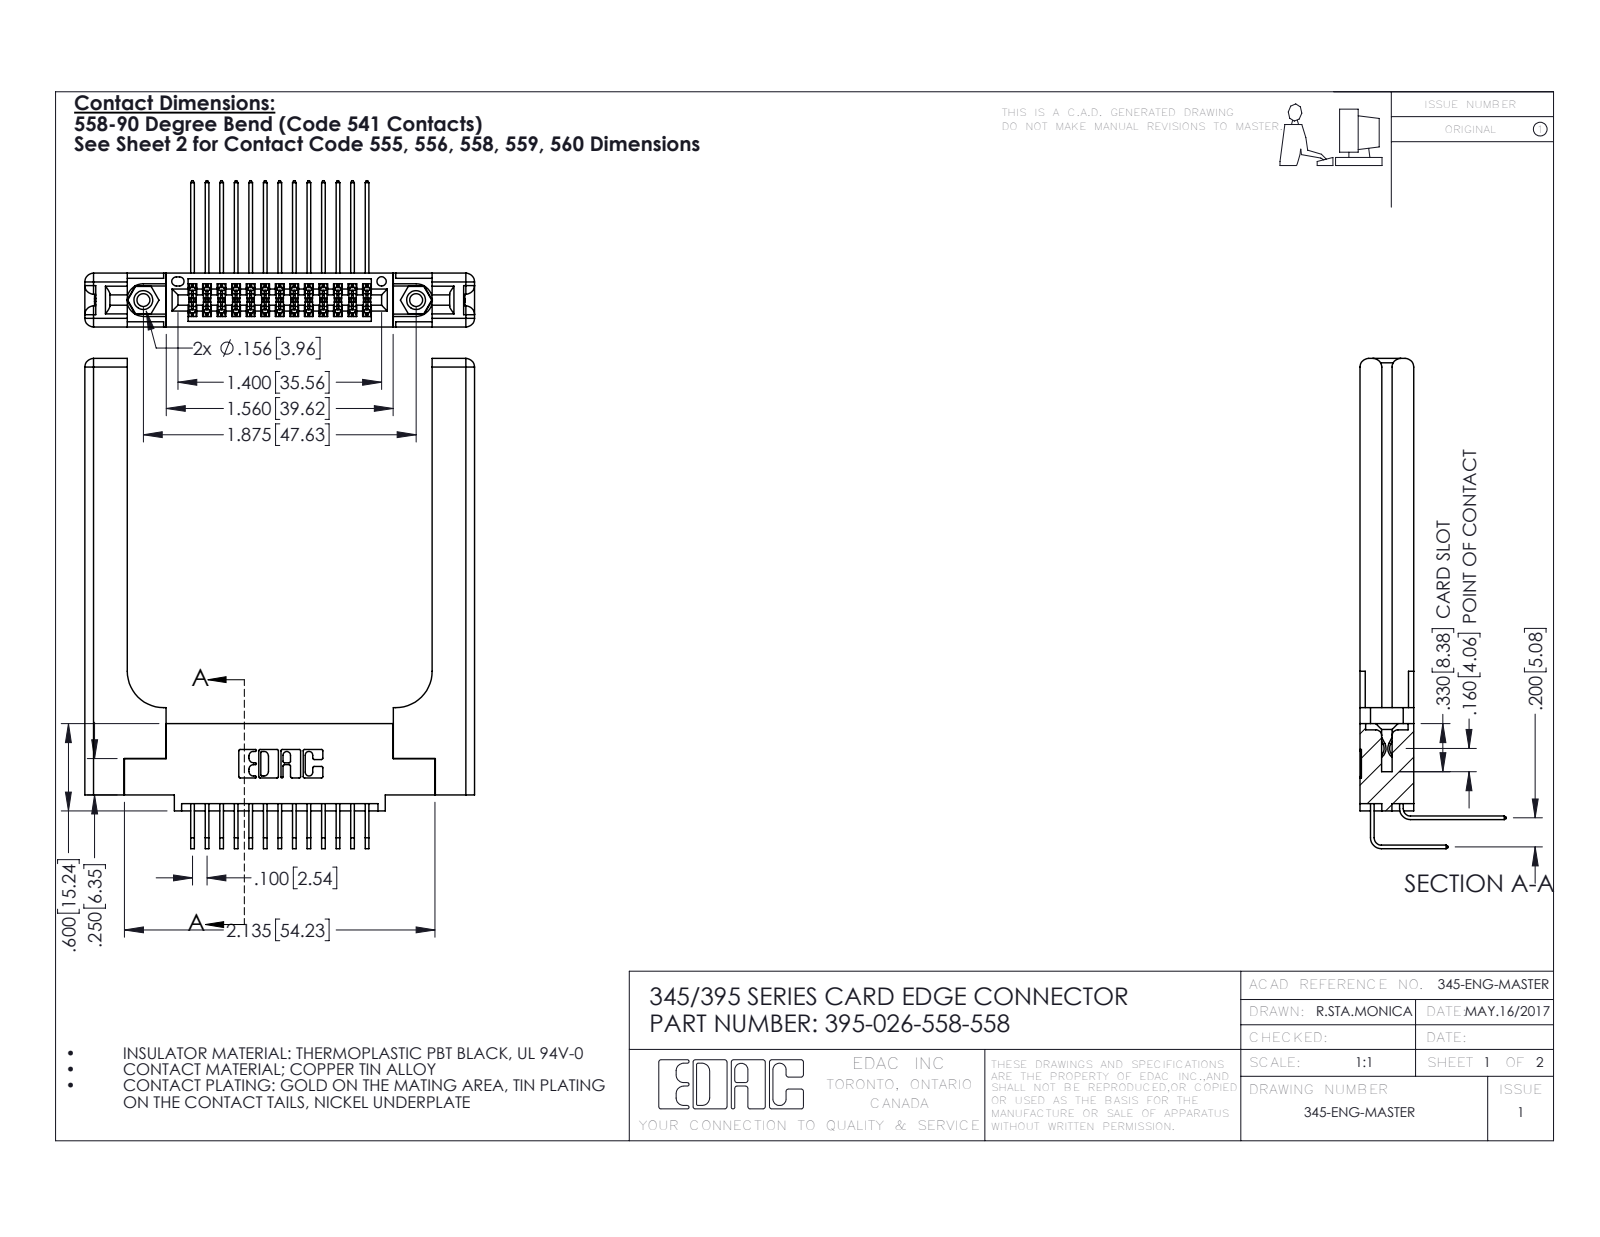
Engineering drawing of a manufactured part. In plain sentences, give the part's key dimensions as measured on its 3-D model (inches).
The part is named "345 Part_0.110 Offset - 0.156 Dia-TH; 395-026-558-558; 345-292-001_558 559 Tail - 1; 345-292-001_558 Tail - 2 (+2 more)". Its 3-D file was written by "SolidWorks 2016 (CONFIG_CONTROL_DESIGN)". It is 31 solids with 1738 faces: 1142 planar, 536 cylindrical and 60 other. Overall it measures 3.369 by 2.679 by 1.005 inches. Its volume is 0.909 cubic inches and its surface area 22.91 square inches. Round holes: 2 of diameter 0.089, 2 of diameter 0.125, 2 of diameter 0.156, 1 of diameter 0.064. Round bosses or shafts: 2 of diameter 0.155. Partial cylindrical surfaces (rounded edges, fillets, slot ends): 40 of radius 0.006, 22 of radius 0.01, 16 of radius 0.06, 6 of radius 0.007, 6 of radius 0.031, 3 of radius 0.026, 2 of radius 0.014, 2 of radius 0.019. The main face-to-face distances are 0.37, 0.072, 0.298, 0.148, 0.15, 0.077, 0.22, 0.2, 0.225, 0.098. The hole center spacings are 0.27, 1.643, 1.875.
